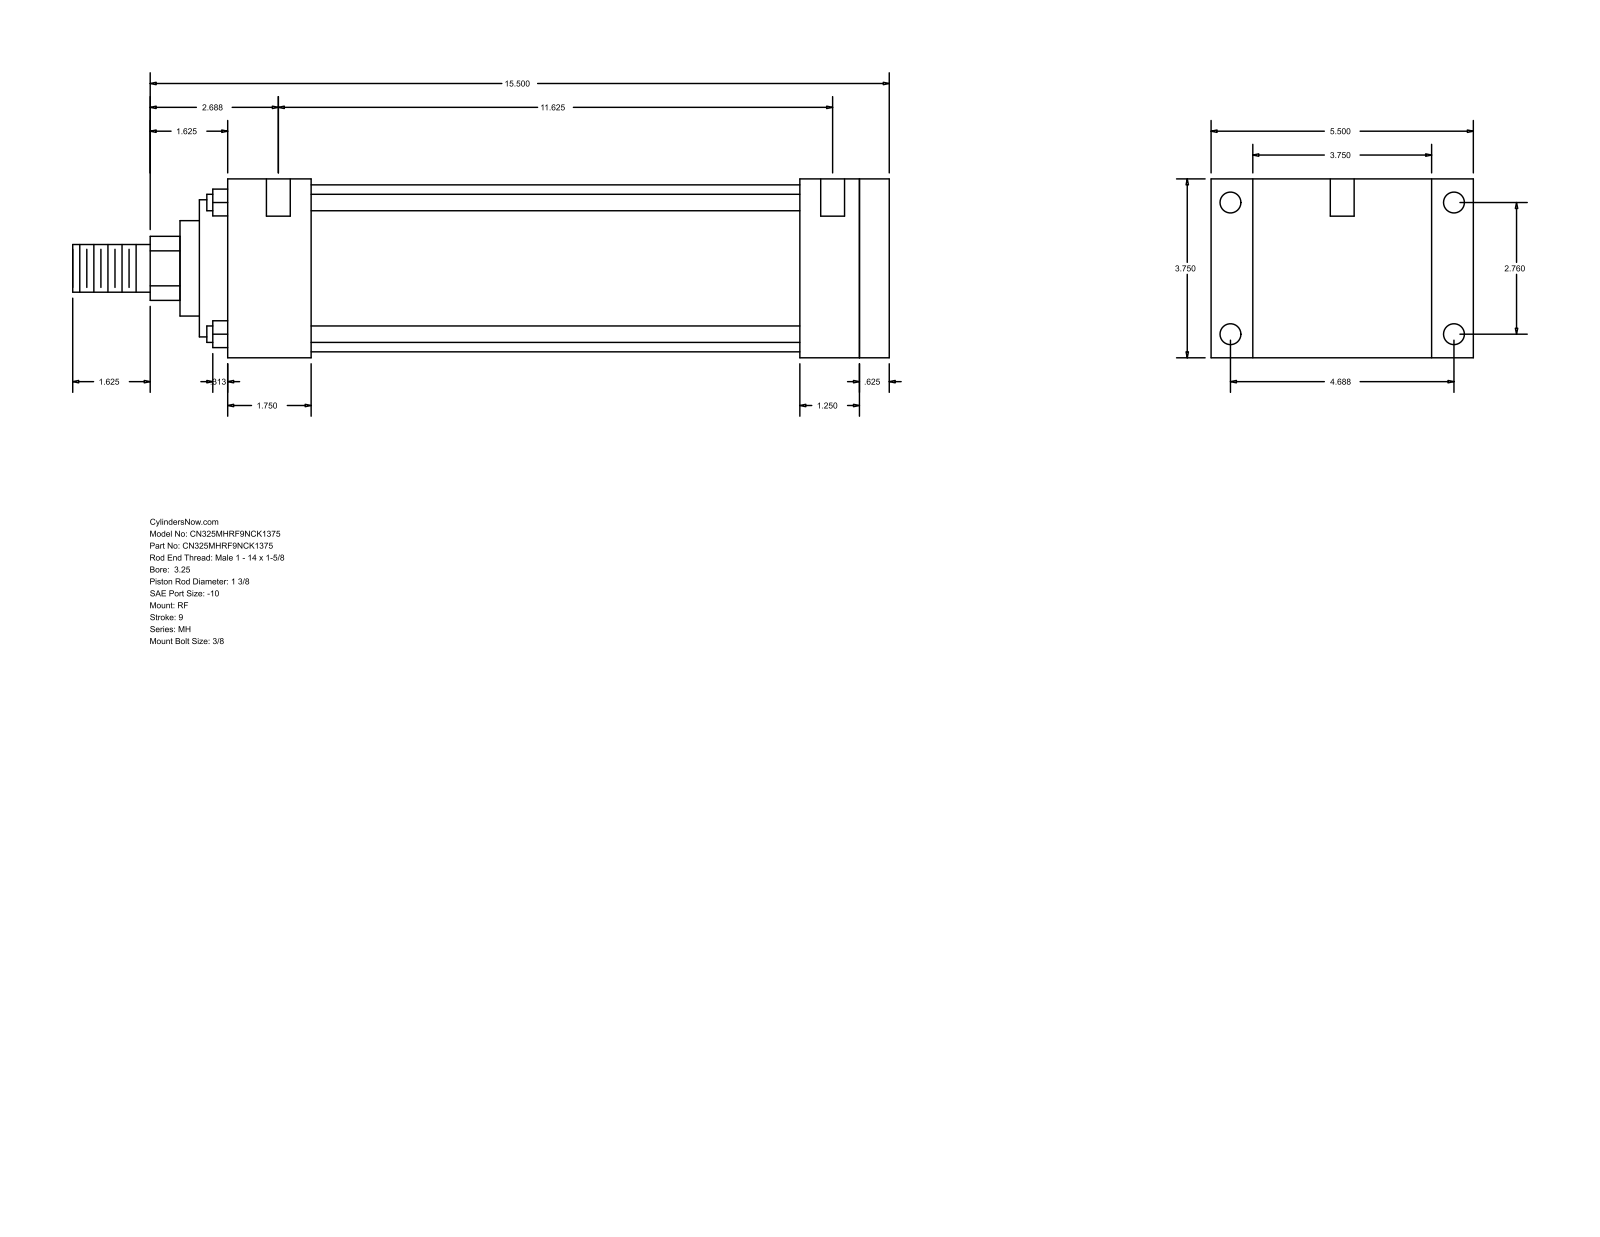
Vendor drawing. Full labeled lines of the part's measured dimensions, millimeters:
Part name (STEP PRODUCT): MH_RF__0325_1.375
STEP written by: GSSL Pune (CONFIG_CONTROL_DESIGN)
Units: millimetres
Bodies: 0 solids, 94 faces (65 planar, 29 cylindrical, 0 other)
Overall size (bounding box): 434.98 × 139.7 × 95.25
Round holes (diameter × count): ⌀5.56 ×4, ⌀11.13 ×4, ⌀12.7 ×2
Round bosses / shafts (diameter × count): ⌀8.76 ×4, ⌀88.9 ×1, ⌀73.03 ×1, ⌀50.8 ×1, ⌀34.92 ×1, ⌀25.4 ×1
Partial cylindrical surfaces — rounded edges, fillets, slot ends (radius × count): R17.06 ×1
Main face-to-face distances: 95.24, 352.43, 15.88, 336.55, 22.23, 117.47, 44.45, 292.1, 307.98, 304.8
Hole centre spacings: 70.1, 119.06, 138.16, 301.63, 1.59, 4.76, 295.28, 296.87
